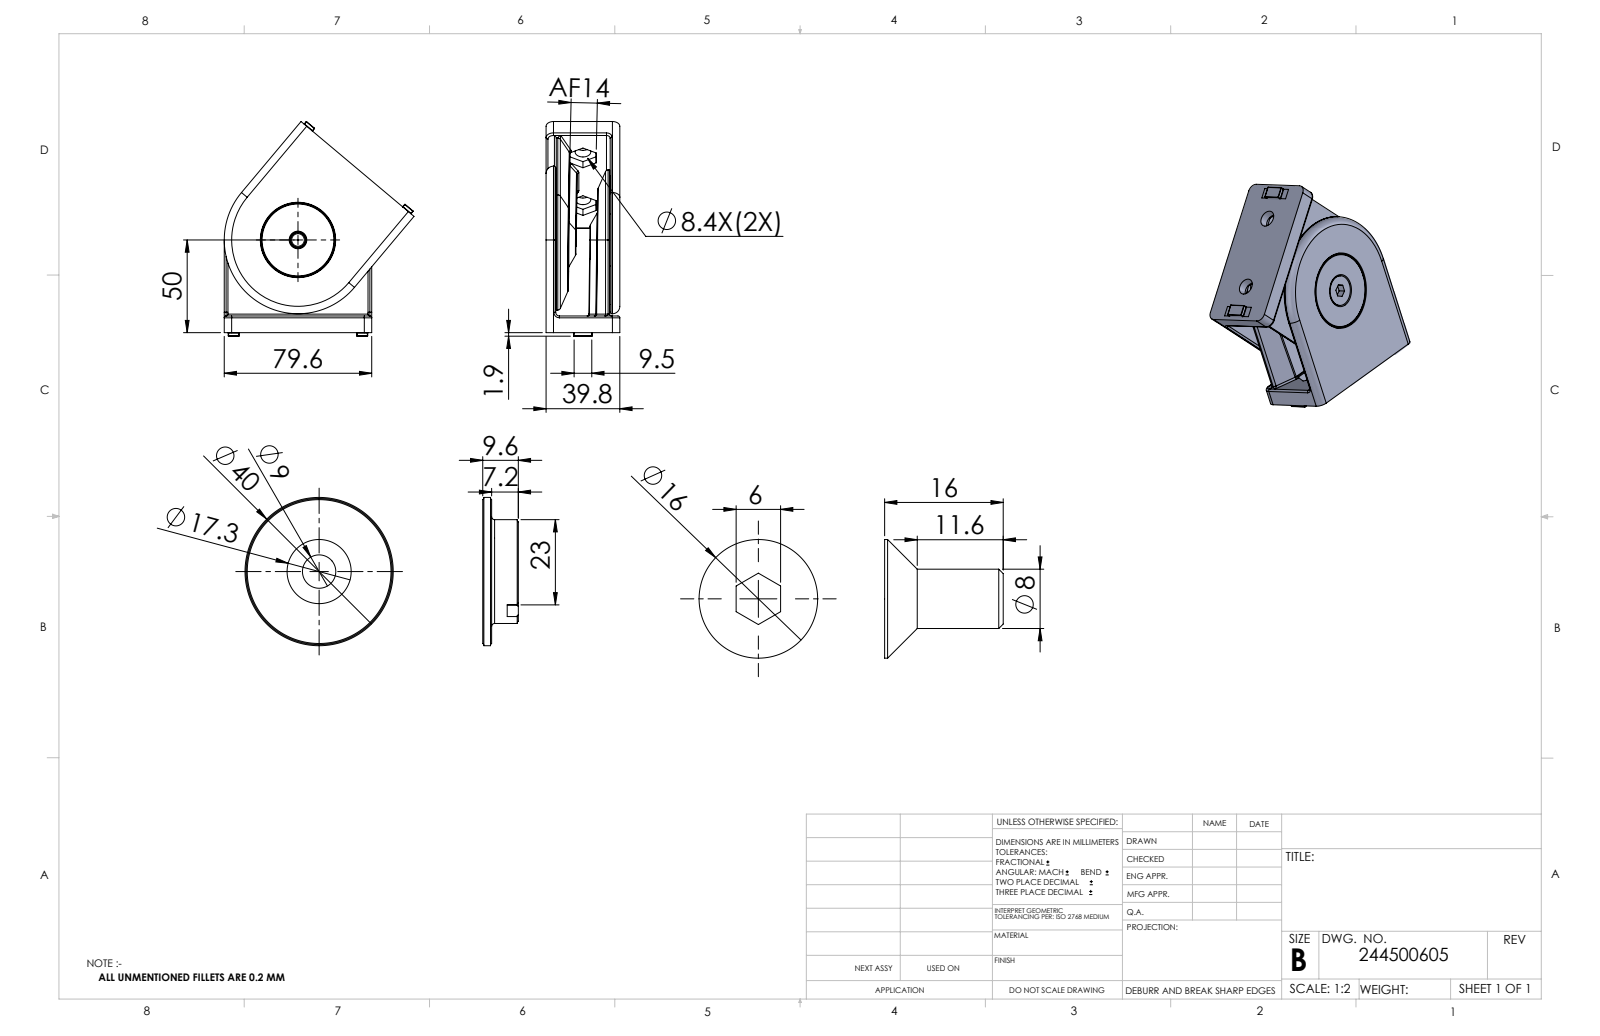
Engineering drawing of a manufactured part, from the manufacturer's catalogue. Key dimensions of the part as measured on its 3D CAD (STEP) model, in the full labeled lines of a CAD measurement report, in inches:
Part name (STEP PRODUCT): 204500605_c_1
STEP written by: SolidWorks 2014 (CONFIG_CONTROL_DESIGN)
Units: inches
Bodies: 11 solids, 1128 faces (268 planar, 353 cylindrical, 507 other)
Overall size (bounding box): 4.558 × 4.033 × 1.567
Volume: 10.7 in³ · Surface area: 122.7 in²
Round holes (diameter × count): ⌀0.268 ×1, ⌀0.327 ×1, ⌀0.354 ×1, ⌀0.787 ×1, ⌀2.378 ×1, ⌀2.756 ×1
Round bosses / shafts (diameter × count): ⌀0.079 ×4, ⌀3.134 ×1, ⌀2.976 ×1, ⌀2.74 ×1, ⌀2.362 ×1, ⌀1.575 ×1, ⌀1.102 ×1, ⌀0.63 ×1
Partial cylindrical surfaces — rounded edges, fillets, slot ends (radius × count): R0.008 ×132, R0.039 ×44, R0.079 ×39, R0.02 ×11, R0.157 ×8, R0.059 ×4, R0.098 ×4
Main face-to-face distances: 0.205, 1.362, 1.567, 1.157, 0.217, 1.35, 1.146, 1.358, 1.134, 0.256
